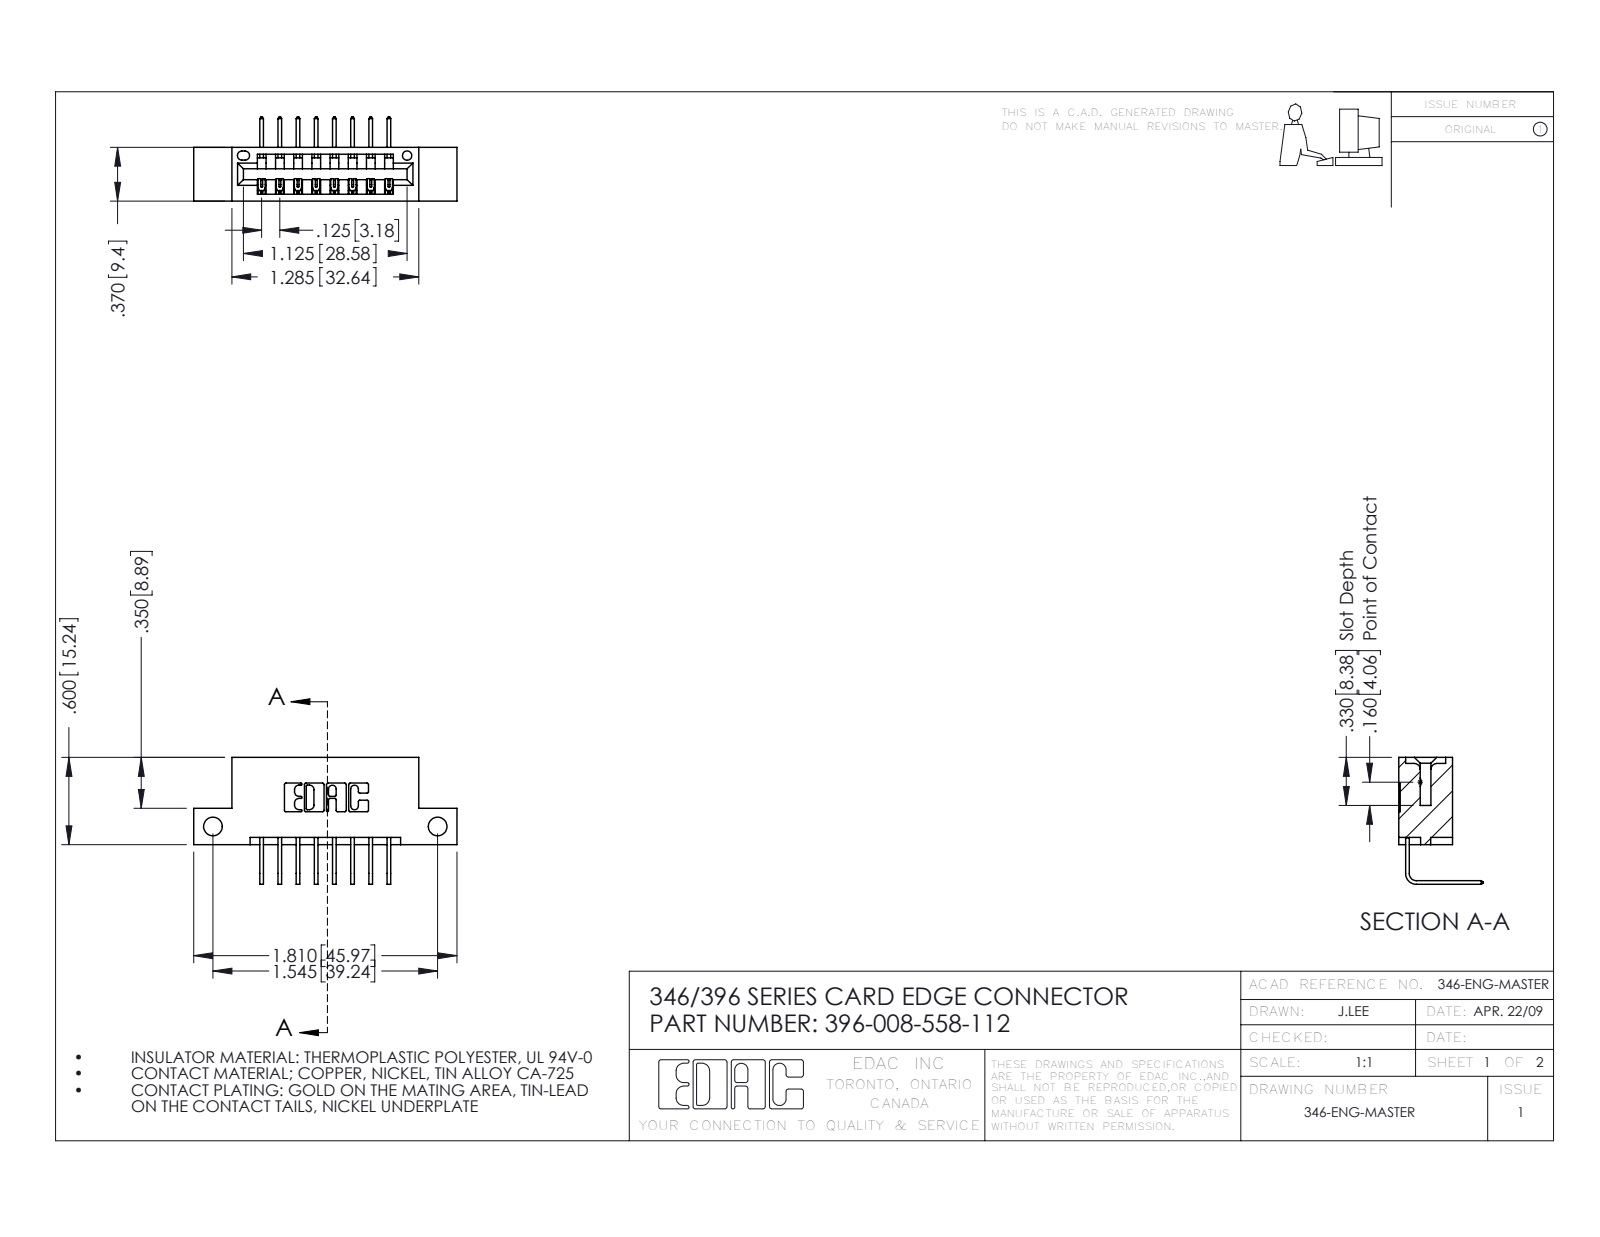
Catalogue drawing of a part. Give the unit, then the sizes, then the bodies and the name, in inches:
Units: inches
Overall size (bounding box): 1.81 × 0.873 × 0.58
Round holes (diameter × count): ⌀0.128 ×2, ⌀0.064 ×1
Partial cylindrical surfaces — rounded edges, fillets, slot ends (radius × count): R0.01 ×22, R0.006 ×16, R0.007 ×6, R0.031 ×6, R0.026 ×3, R0.031 ×2, R0.04 ×2, R0.014 ×1
Main face-to-face distances: 0.25, 0.322, 0.37, 0.048, 0.298, 0.025, 0.5, 0.148, 0.222, 0.1
Hole centre spacings: 1.545
Volume: 0.251 in³ · Surface area: 7.406 in²
Bodies: 9 solids, 602 faces (412 planar, 190 cylindrical, 0 other)
Part name (STEP PRODUCT): 396-008-558-112; 346 Part_Flush Mounting Lugs - Side Mount; 345-292-001_558 Tail - 2
STEP written by: SolidWorks 2016 (CONFIG_CONTROL_DESIGN)
